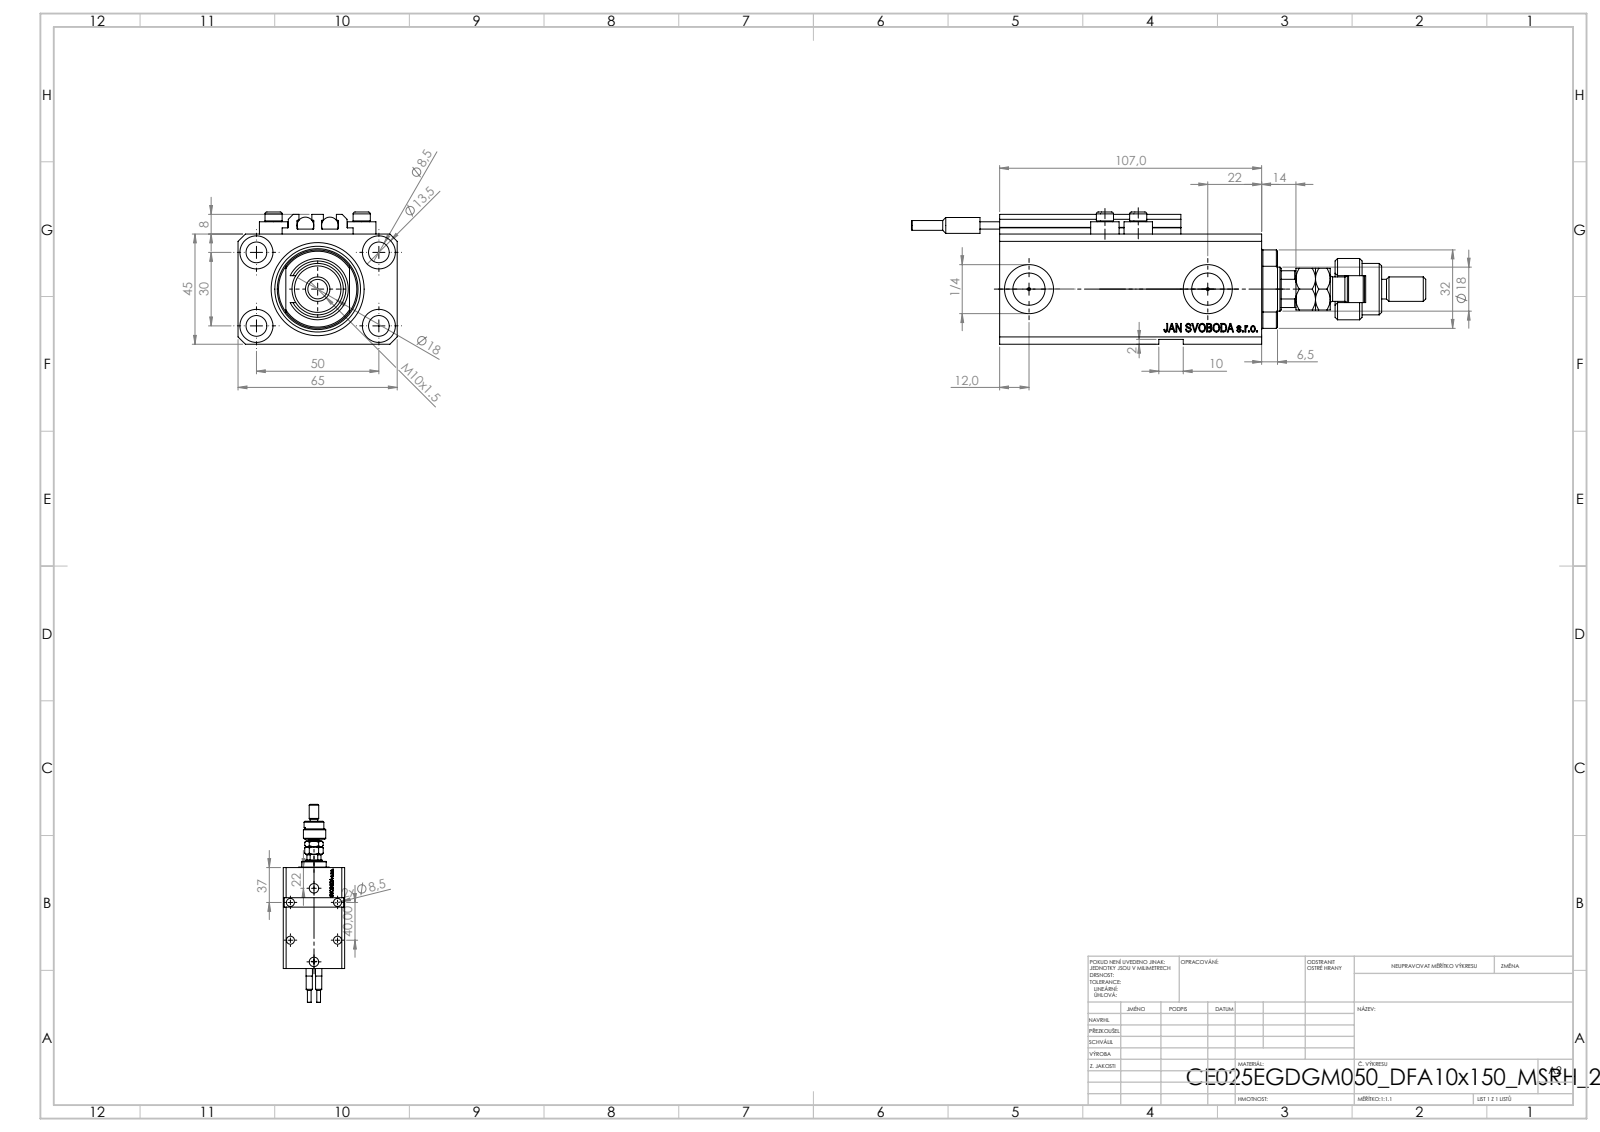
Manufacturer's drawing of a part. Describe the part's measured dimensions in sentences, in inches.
The part is named "MFA; V250CE_E_Body; FEMALE_PART_FOR_DFA; V250CE_C_VCP (+3 more)". Its 3-D file was written by "SolidWorks 2019 (CONFIG_CONTROL_DESIGN)". It is 12 solids with 1240 faces: 575 planar, 183 cylindrical and 482 other. Overall it measures 8.268 by 2.559 by 2.126 inches. Its volume is 17.4 cubic inches and its surface area 133.6 square inches. Round holes: 9 of diameter 0.335, 4 of diameter 0.049, 4 of diameter 0.157, 4 of diameter 0.531, 2 of diameter 0.394, 2 of diameter 0.518, 2 of diameter 0.787, 1 of diameter 0.709, 1 of diameter 1.496. Round bosses or shafts: 4 of diameter 0.457, 4 of diameter 0.276, 2 of diameter 0.268, 2 of diameter 0.256, 2 of diameter 0.157, 1 of diameter 0.984, 1 of diameter 0.827, 1 of diameter 0.63. Partial cylindrical surfaces (rounded edges, fillets, slot ends): 10 of radius 0.008, 1 of radius 0.217, 1 of radius 0.335, 1 of radius 0.344, 1 of radius 0.63. The main face-to-face distances are 1.772, 2.559, 0.551, 0.079, 1.85, 0.118, 3.661, 4.213, 0.197, 0.394. The hole center spacings are 1.148, 1.969, 0.535, 0.581, 0.595, 1.083, 1.098, 1.181.
